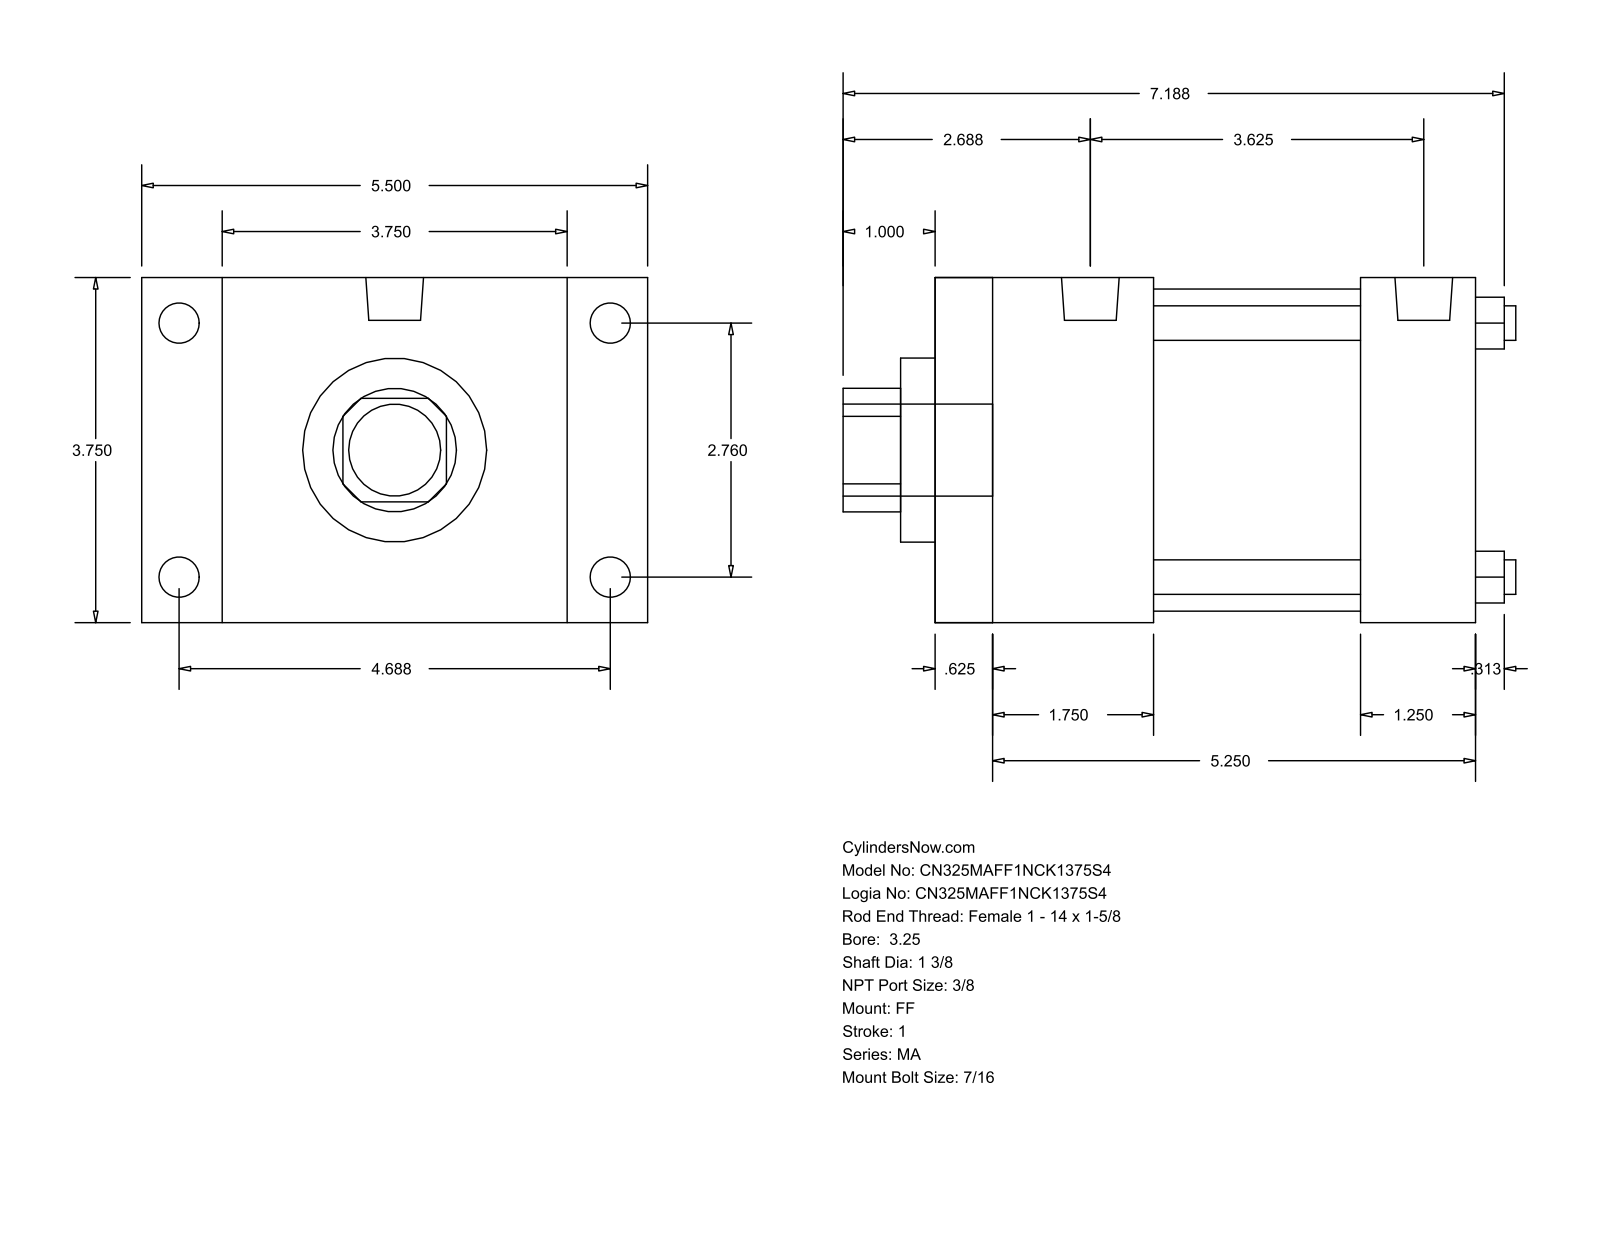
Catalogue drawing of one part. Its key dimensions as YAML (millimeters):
part_name: "MA_FF__0325_1.375"
step_written_by: "GSSL Pune (CONFIG_CONTROL_DESIGN)"
units: millimeters
bodies: {solids: 0, faces: 92, planar: 64, cylindrical: 28, other: 0}
overall_size: [185.74, 139.7, 95.25]
round_holes:
  - {diameter: 9.53, count: 4}
  - {diameter: 34.92, count: 1}
  - {diameter: 50.8, count: 1}
  - {diameter: 88.9, count: 1}
round_bosses_or_shafts:
  - {diameter: 11.11, count: 8}
  - {diameter: 15.93, count: 2}
  - {diameter: 25.4, count: 1}
partial_cylinders:
  - {radius: 17.06, count: 1}
face_to_face_distances: [95.24, 149.22, 15.87, 133.35, 22.23, 117.47, 60.32, 117.48, 44.45, 101.61]
hole_center_spacings: [49.57, 70.1, 99.14]
